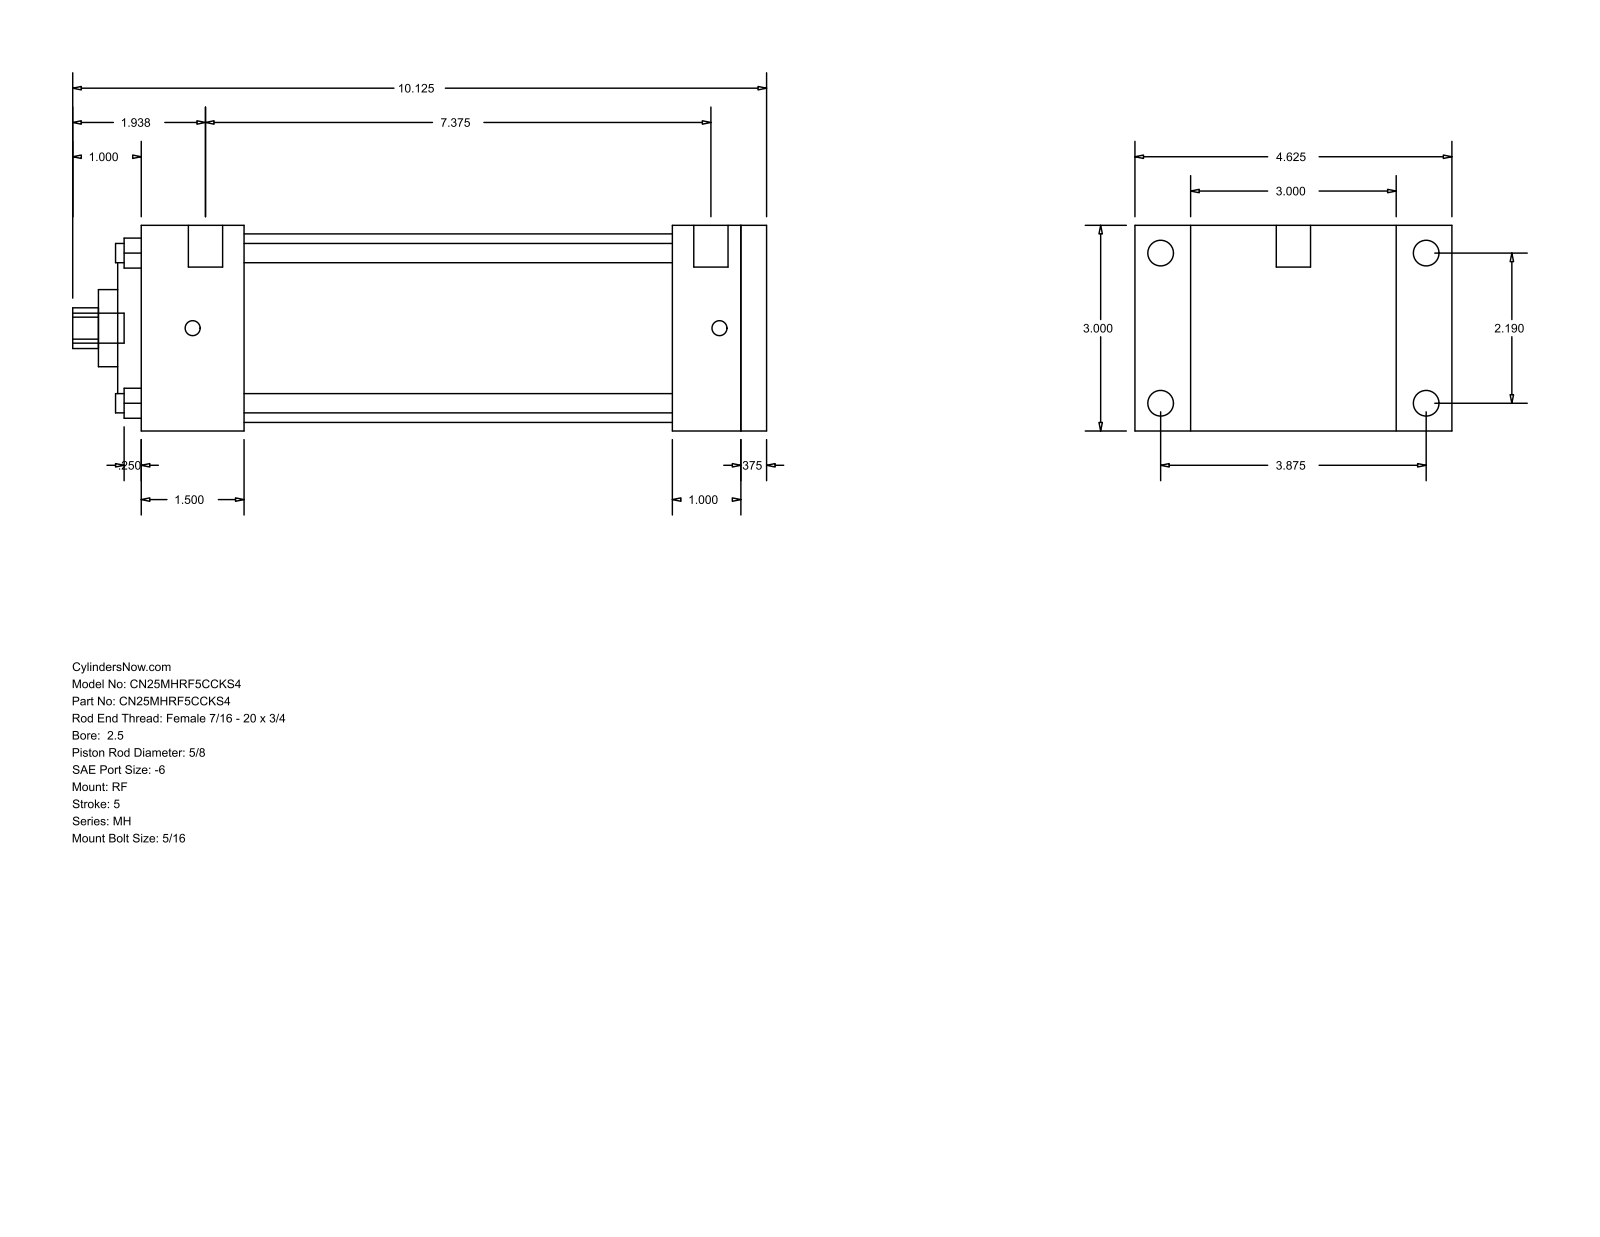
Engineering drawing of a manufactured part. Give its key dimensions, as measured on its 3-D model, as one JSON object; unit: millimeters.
{"part_name": "MH_RF__0250_0.625", "step_written_by": "GSSL Pune (CONFIG_CONTROL_DESIGN)", "units": "millimeters", "bodies": {"solids": 0, "faces": 94, "planar": 65, "cylindrical": 29, "other": 0}, "overall_size": [257.18, 117.47, 76.2], "round_holes": [[7.14, 4], [15.88, 1], [28.57, 1], [55.55, 1], [69.85, 1]], "round_bosses_or_shafts": [[9.53, 4], [5.56, 4], [12.7, 2], [11.11, 1]], "partial_cylinders_radius": [[7.54, 1]], "face_to_face_distances": [76.2, 9.53, 231.78, 222.25, 25.4, 196.85, 34.93, 38.1, 158.75, 184.15], "hole_center_spacings": [39.33, 55.62, 78.66]}
